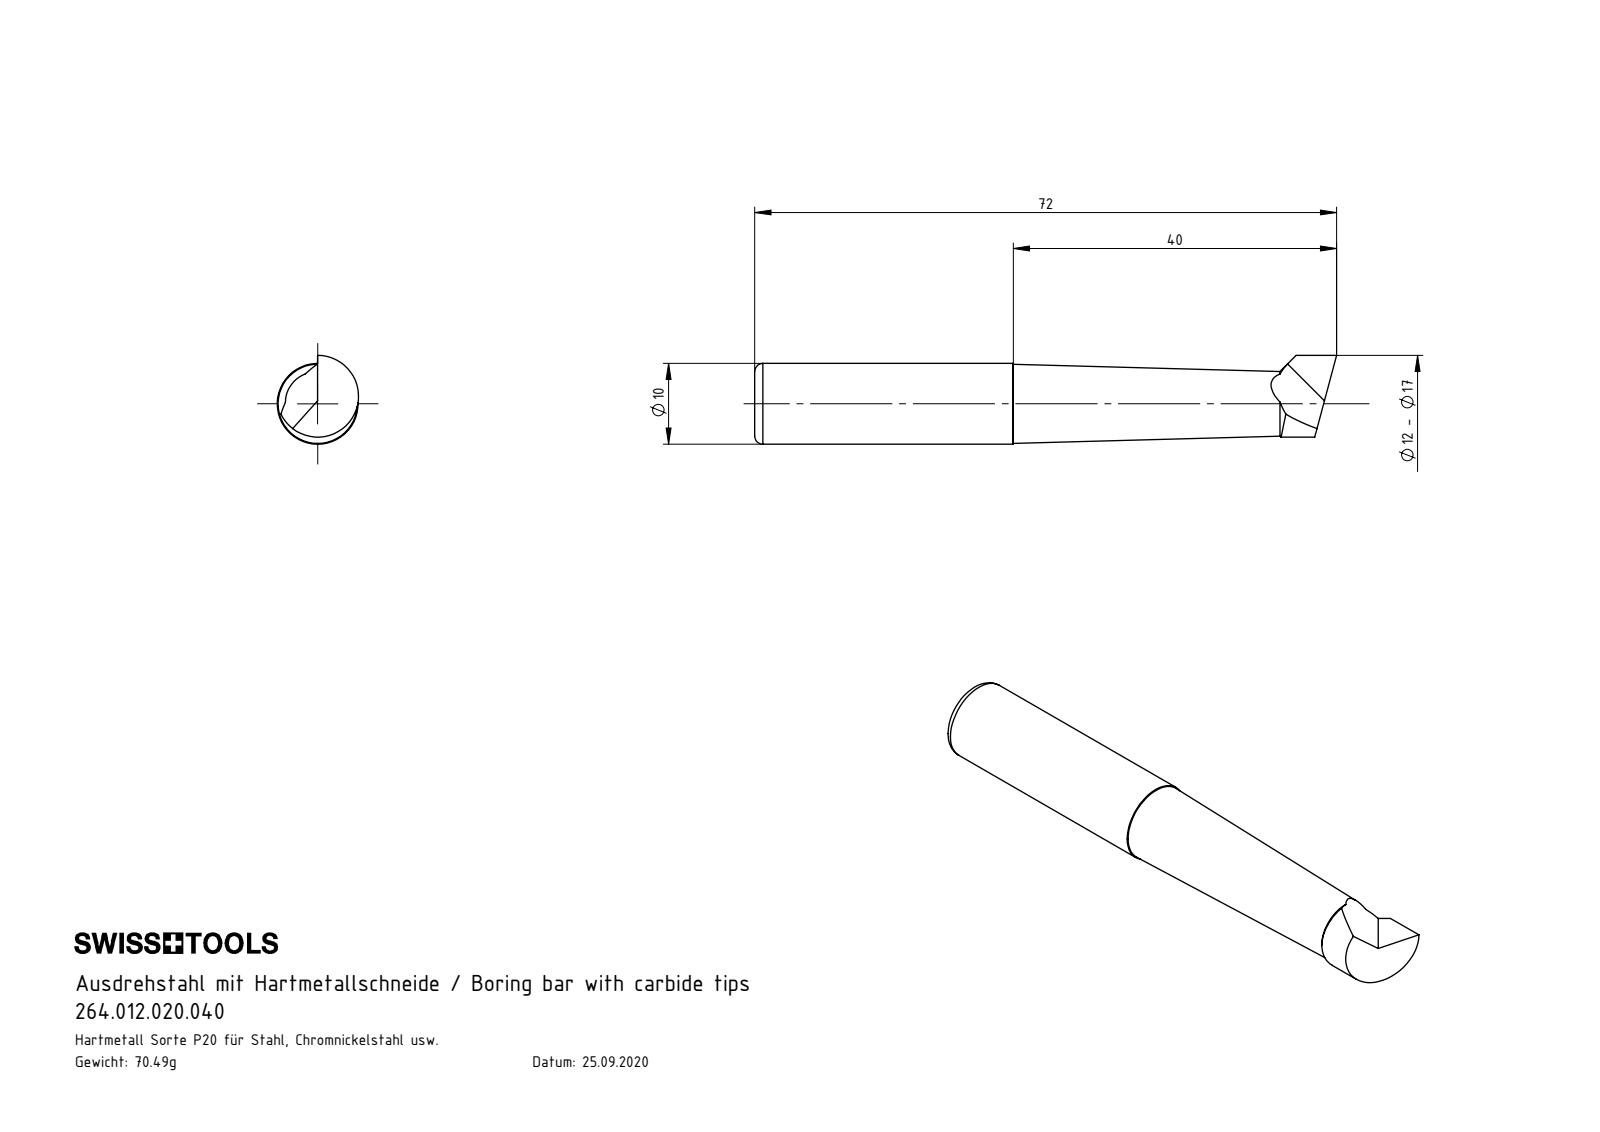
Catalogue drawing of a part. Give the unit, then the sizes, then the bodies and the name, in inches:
Units: inches
Overall size (bounding box): 2.835 × 0.433 × 0.396
Round bosses / shafts (diameter × count): ⌀0.394 ×1
Partial cylindrical surfaces — rounded edges, fillets, slot ends (radius × count): R0.199 ×1
Volume: 0.297 in³ · Surface area: 3.436 in²
Bodies: 1 solid, 10 faces (4 planar, 2 cylindrical, 4 other)
Part name (STEP PRODUCT): U10.B12.002.040
STEP written by: SolidWorks 2017 (AUTOMOTIVE_DESIGN)
